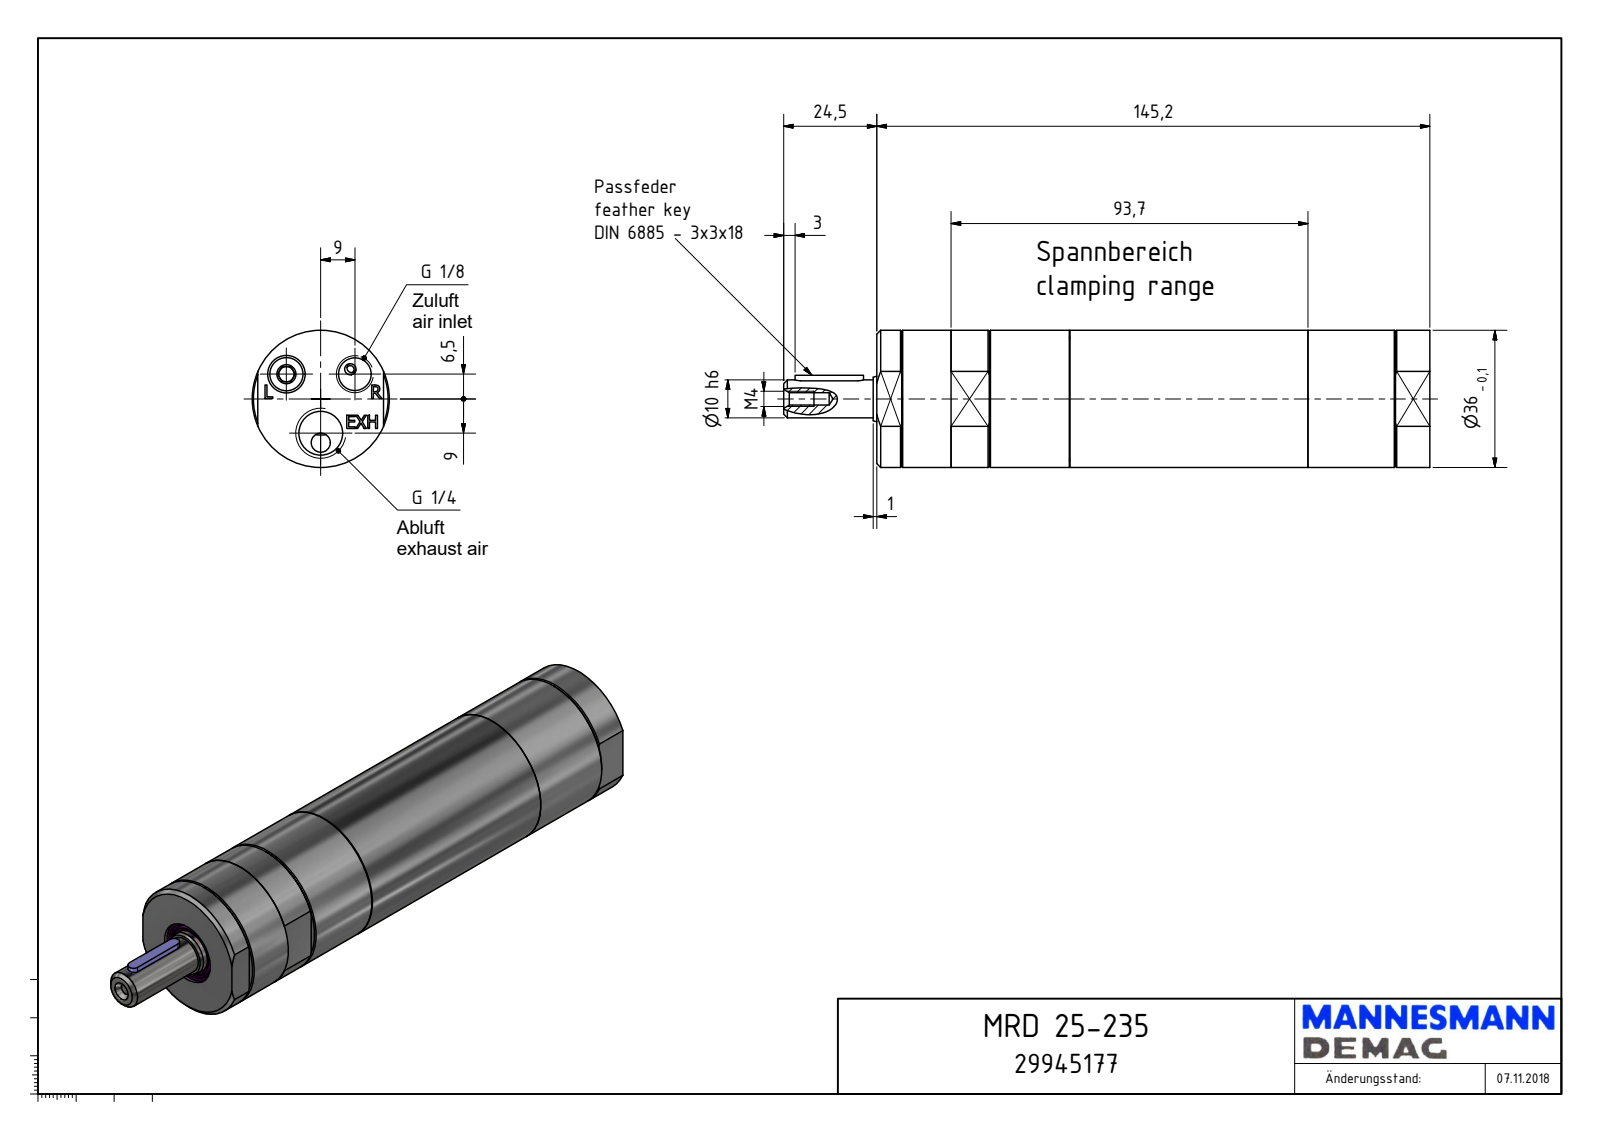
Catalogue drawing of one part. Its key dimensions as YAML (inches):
part_name: "MRD 25-235_29945177"
step_written_by: "Autodesk Inventor 2018 (AUTOMOTIVE_DESIGN)"
units: inches
bodies: {solids: 1, faces: 155, planar: 101, cylindrical: 22, other: 32}
overall_size: [6.681, 1.417, 1.417]
volume: 8.963
surface_area: 32.5
round_holes:
  - {diameter: 0.337, count: 2}
  - {diameter: 0.128, count: 1}
  - {diameter: 0.157, count: 1}
  - {diameter: 0.451, count: 1}
  - {diameter: 0.61, count: 1}
  - {diameter: 0.669, count: 1}
round_bosses_or_shafts:
  - {diameter: 1.417, count: 1}
  - {diameter: 1.26, count: 1}
  - {diameter: 0.47, count: 1}
  - {diameter: 0.394, count: 1}
partial_cylinders:
  - {radius: 0.059, count: 2}
face_to_face_distances: [5.717, 1.299, 5.326, 0.39, 1.988, 3.338, 3.728, 1.996, 3.33, 3.72]
hole_center_spacings: [0.437, 0.706, 0.354, 0.709]
